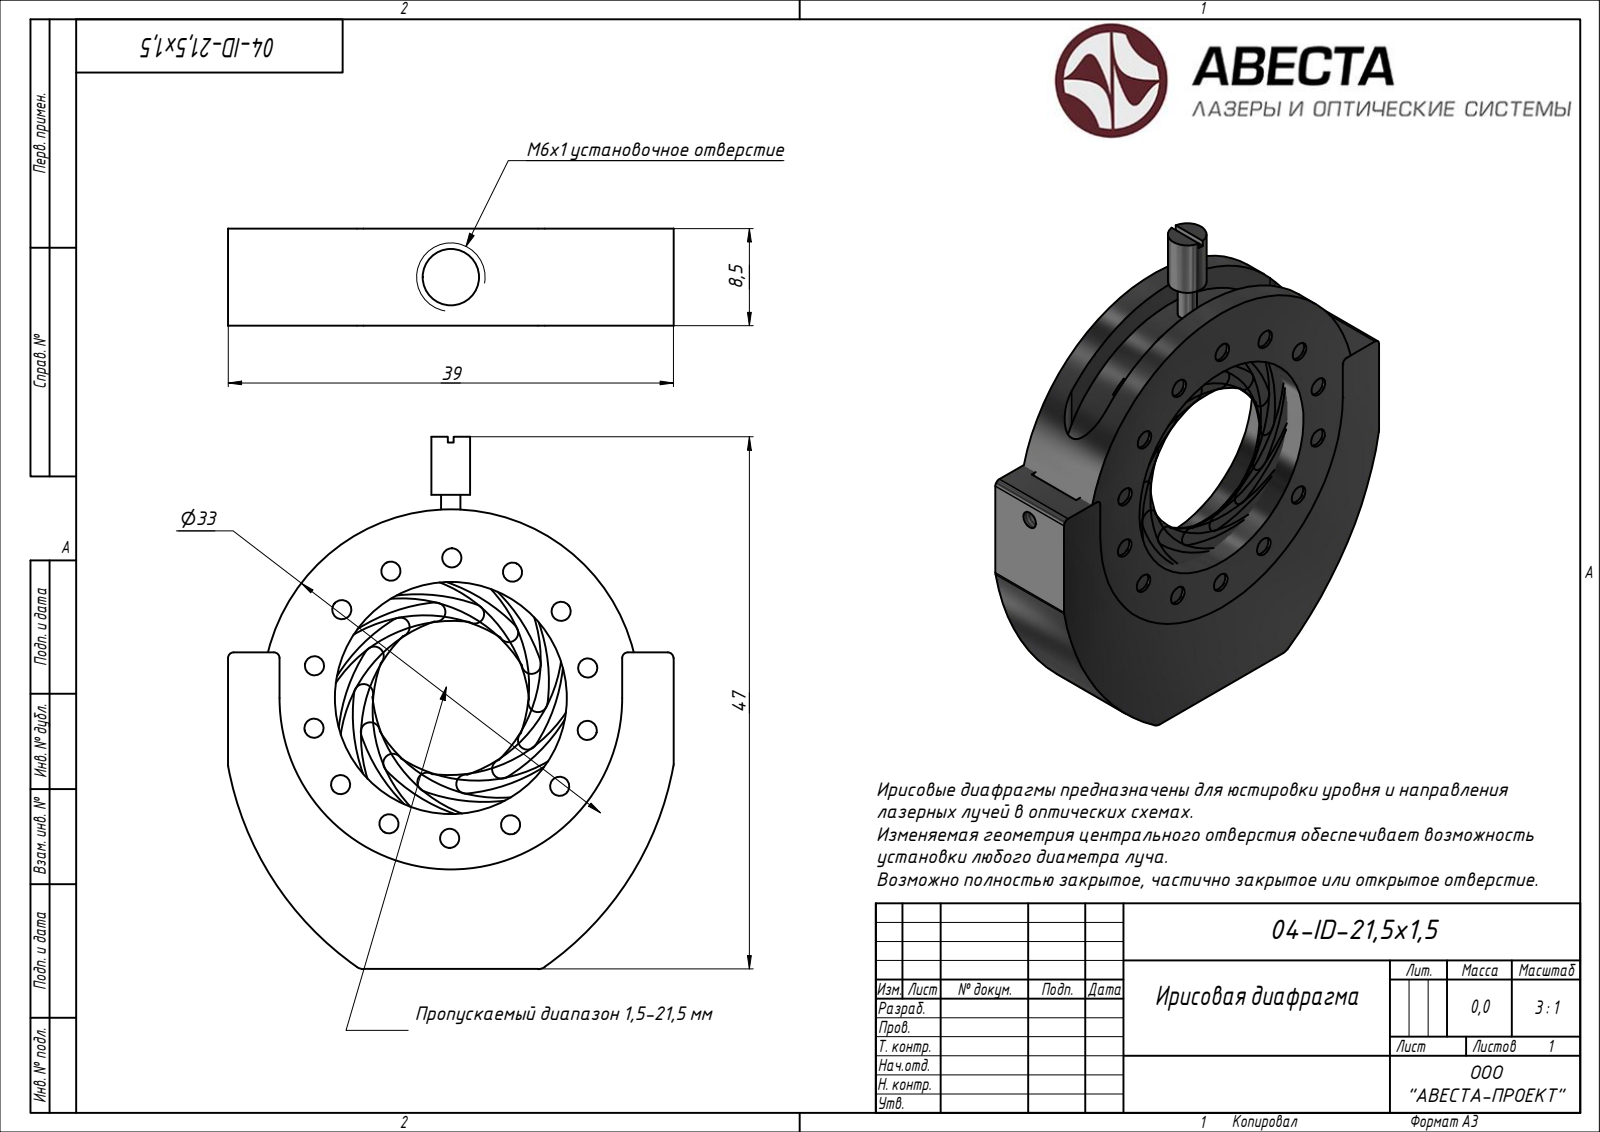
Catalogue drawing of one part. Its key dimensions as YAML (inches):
step_written_by: "ST-DEVELOPER v15 (AUTOMOTIVE_DESIGN)"
units: inches
bodies: {solids: 0, faces: 322, planar: 173, cylindrical: 0, other: 149}
overall_size: [1.833, 1.535, 0.335]
face_to_face_distances: [0.084, 0.25, 0.335, 0.334, 0.167, 0.251, 0.084, 0.067, 0.078, 0.077]
